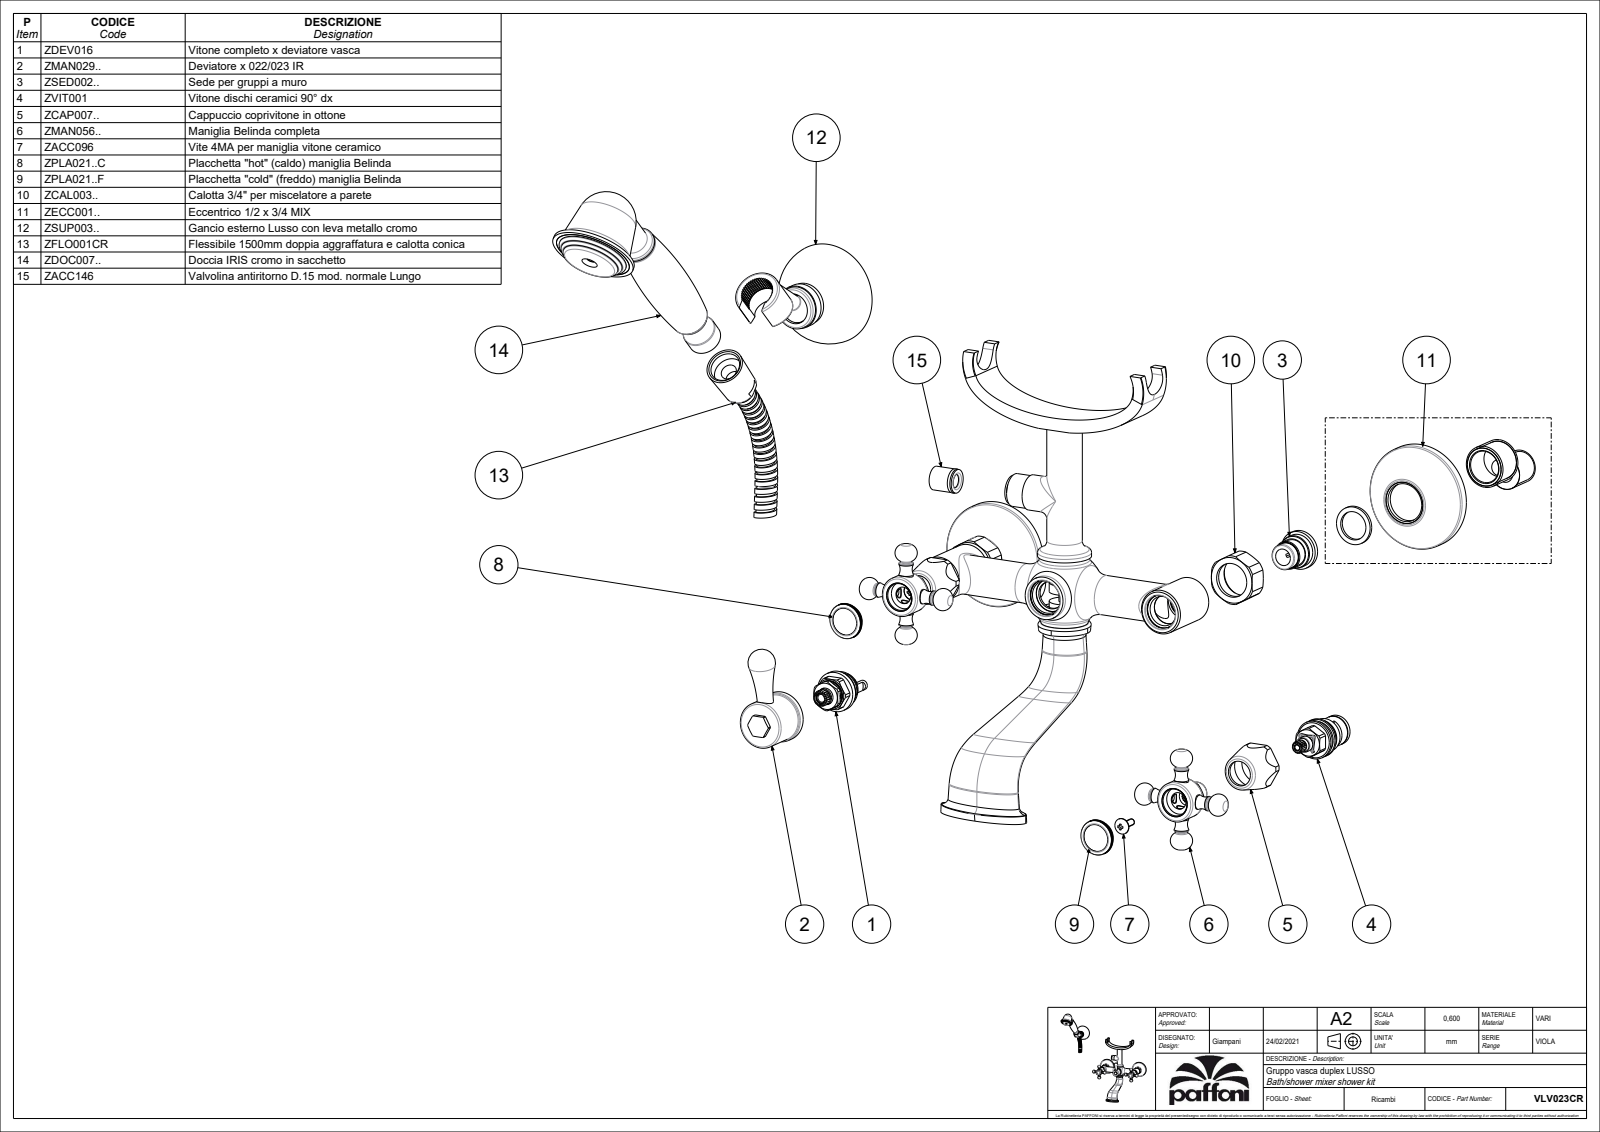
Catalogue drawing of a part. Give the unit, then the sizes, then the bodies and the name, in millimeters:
Units: millimetres
Overall size (bounding box): 413.37 × 343.25 × 243.29
Round holes (diameter × count): ⌀15.7 ×2, ⌀17 ×2, ⌀18.63 ×2, ⌀19 ×2, ⌀20.8 ×2, ⌀21.5 ×2, ⌀23 ×2, ⌀9 ×1, ⌀14.5 ×1, ⌀15.4 ×1, ⌀15.5 ×1, ⌀17.2 ×1
Round bosses / shafts (diameter × count): ⌀14 ×3, ⌀13 ×3, ⌀9 ×3, ⌀7 ×3, ⌀65.5 ×2, ⌀29 ×2, ⌀27.8 ×2, ⌀27 ×2
Partial cylindrical surfaces — rounded edges, fillets, slot ends (radius × count): R3.5 ×2, R10 ×2, R11 ×2, R14.5 ×2, R15.5 ×2, R7.35 ×1
Main face-to-face distances: 26.5, 66.95, 40.45, 33.7, 6.75, 33.25, 29, 35.2, 72.2, 5.25
Hole centre spacings: 79, 158
Volume: 524 896 mm³ · Surface area: 186 807 mm²
Bodies: 4 solids, 1667 faces (640 planar, 464 cylindrical, 563 other)
Part name (STEP PRODUCT): VLV023CR
STEP written by: CREO PARAMETRIC BY PTC INC, 2020044 (CONFIG_CONTROL_DESIGN)
